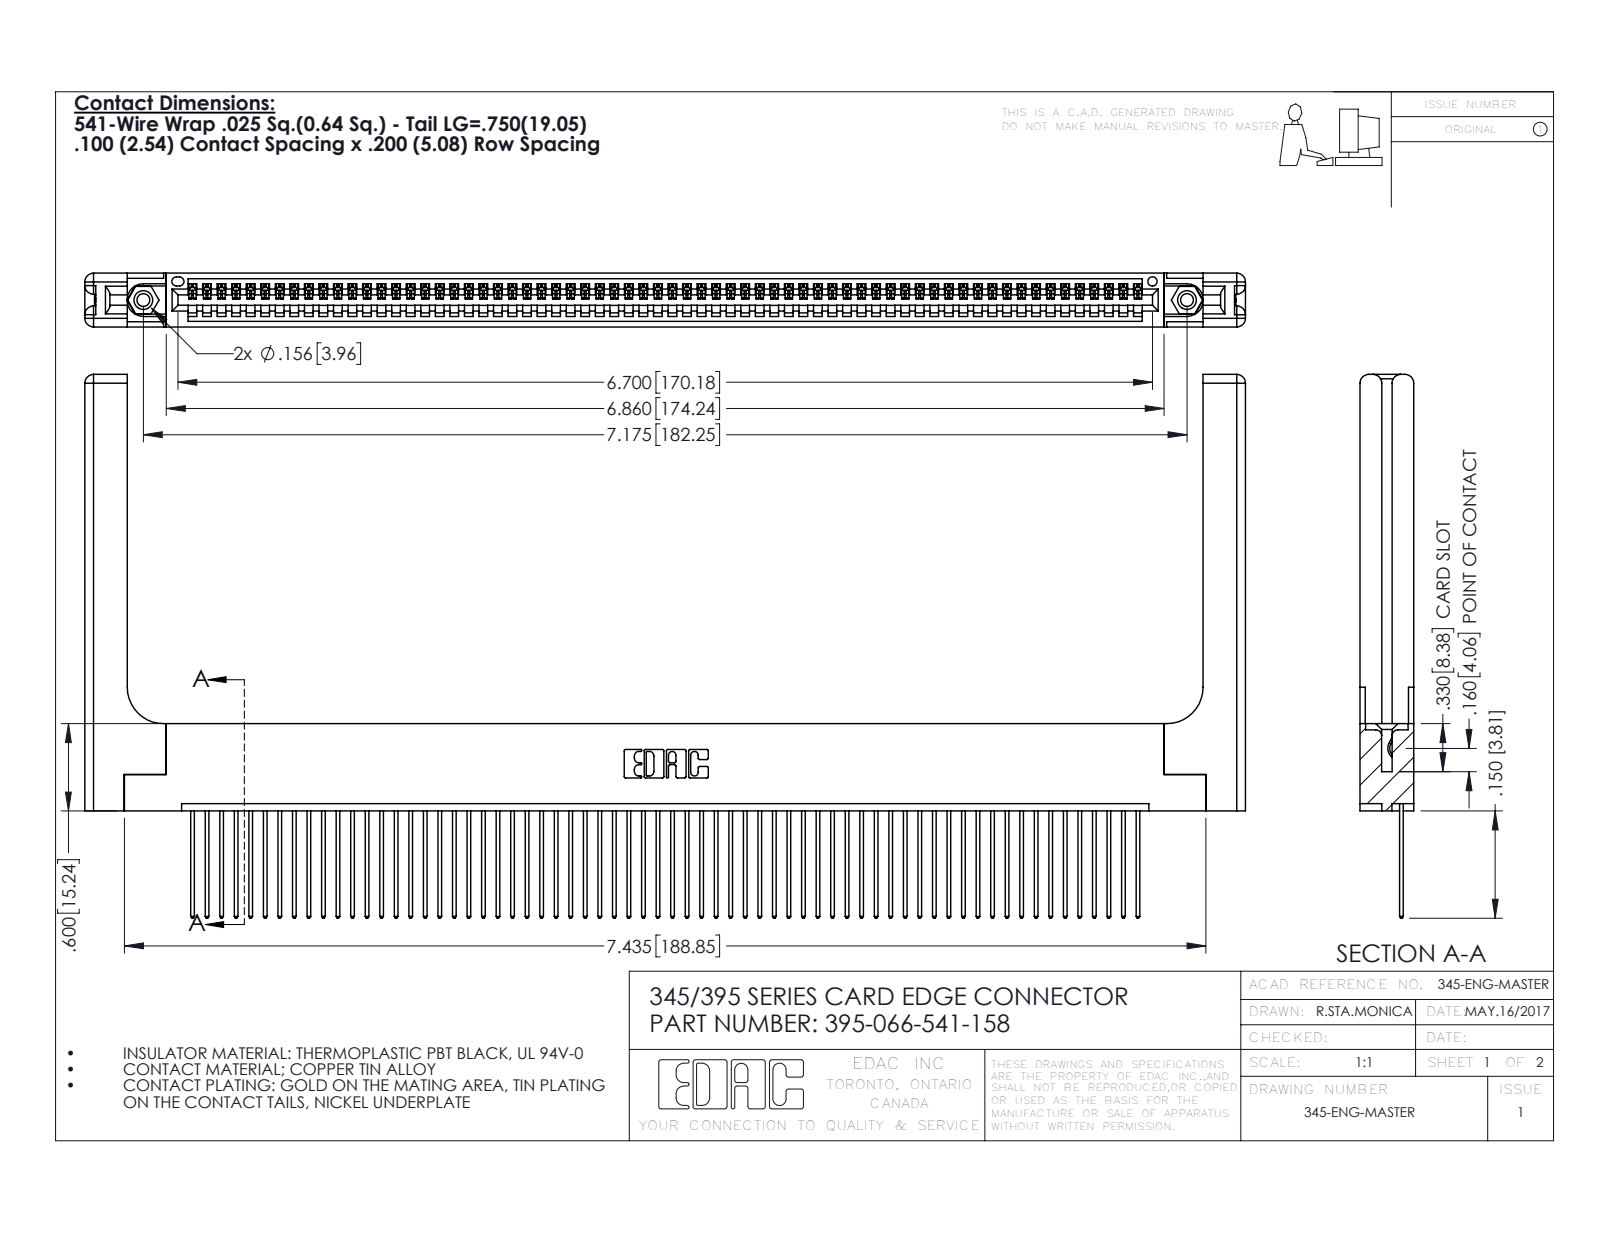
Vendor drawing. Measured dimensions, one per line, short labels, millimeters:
name: 395-066-541-158; 345-250-001_345-250-001-102; 345 Part_Flush Mounting Lugs - 0.156 Dia-TH; 345-220-058_345-220-058 (+1 more)
written by: SolidWorks 2016 (CONFIG_CONTROL_DESIGN)
unit: mm
bodies: 71 solids, 4210 faces (2868 planar, 1282 cylindrical, 60 other)
size: 202.7 × 94.9 × 9.4
volume: 28 170 mm³; area: 33 050 mm²
holes: 2× ⌀2.3, 2× ⌀3.2, 2× ⌀4, 1× ⌀1.6
bosses: 2× ⌀3.9
rounds: 132× R0.2, 132× R0.3, 22× R0.3, 16× R1.5, 6× R0.2, 6× R0.8, 3× R0.7, 2× R0.8
face distances: 1.8, 7.6, 9.4, 2.5, 6.9, 0.6, 5.1, 5.7, 3.8, 3.8
hole spacings: 6.9, 176.3, 182.2
